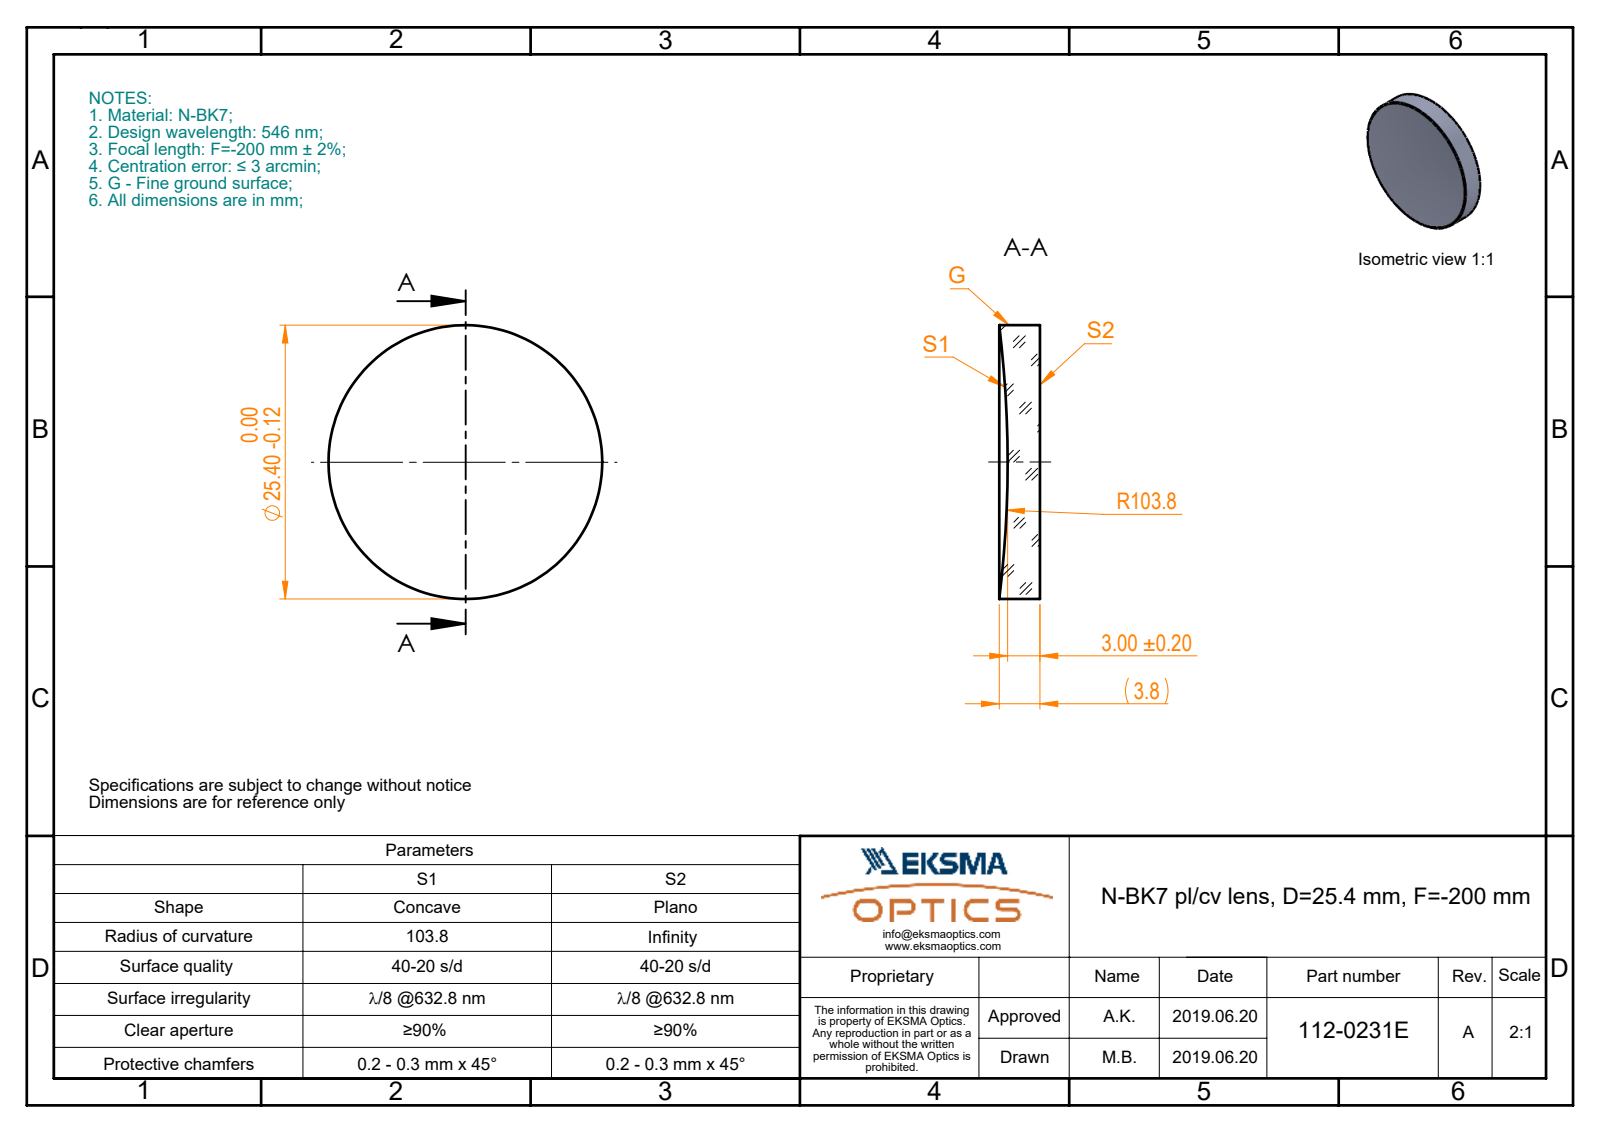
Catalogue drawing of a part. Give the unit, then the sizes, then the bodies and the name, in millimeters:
Units: millimetres
Overall size (bounding box): 25.4 × 25.4 × 3.78
Round bosses / shafts (diameter × count): ⌀25.4 ×1
Volume: 1 718 mm³ · Surface area: 1 317 mm²
Bodies: 1 solid, 5 faces (1 planar, 2 cylindrical, 2 other)
Part name (STEP PRODUCT): 112-0231E BK7 pl-cv 25.4 F-200
STEP written by: SolidWorks 2017 (CONFIG_CONTROL_DESIGN)
